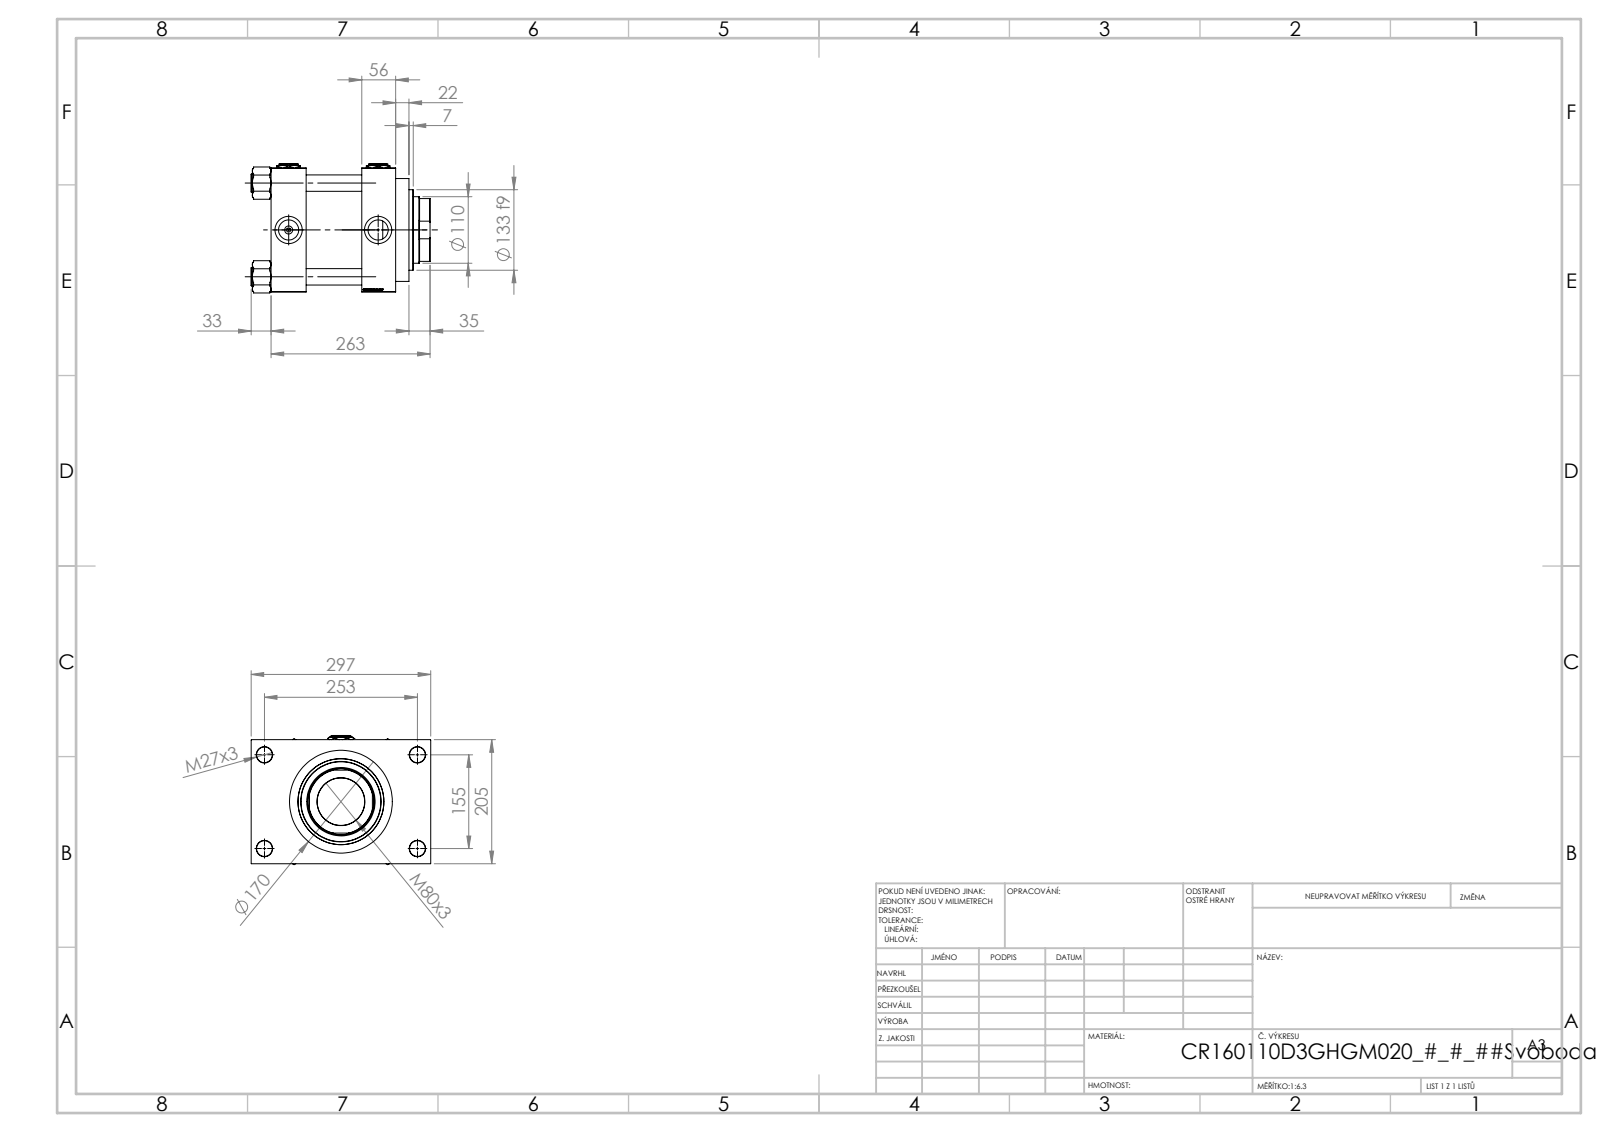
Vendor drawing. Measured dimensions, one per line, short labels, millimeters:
name: V215_VC_A; V215CR_D_TYCINKA; V215CR_VCP_D; V215CR_D_Body (+2 more)
written by: SolidWorks 2019 (CONFIG_CONTROL_DESIGN)
unit: mm
bodies: 13 solids, 1252 faces (593 planar, 99 cylindrical, 560 other)
size: 297 × 296 × 213.57
volume: 8 095 000 mm³; area: 790 926 mm²
holes: 4× ⌀26, 4× ⌀27, 4× ⌀33.24, 4× ⌀45, 3× ⌀7, 1× ⌀78.5, 1× ⌀110, 1× ⌀113, 1× ⌀120, 1× ⌀142, 1× ⌀160
bosses: 4× ⌀30, 1× ⌀170, 1× ⌀166, 1× ⌀133
rounds: 1× R54
face distances: 58, 150, 92, 205, 148, 56, 206, 46, 251, 72
hole spacings: 49.05, 109.53, 148.35, 154.9, 162.53, 203.95, 256.13, 148
